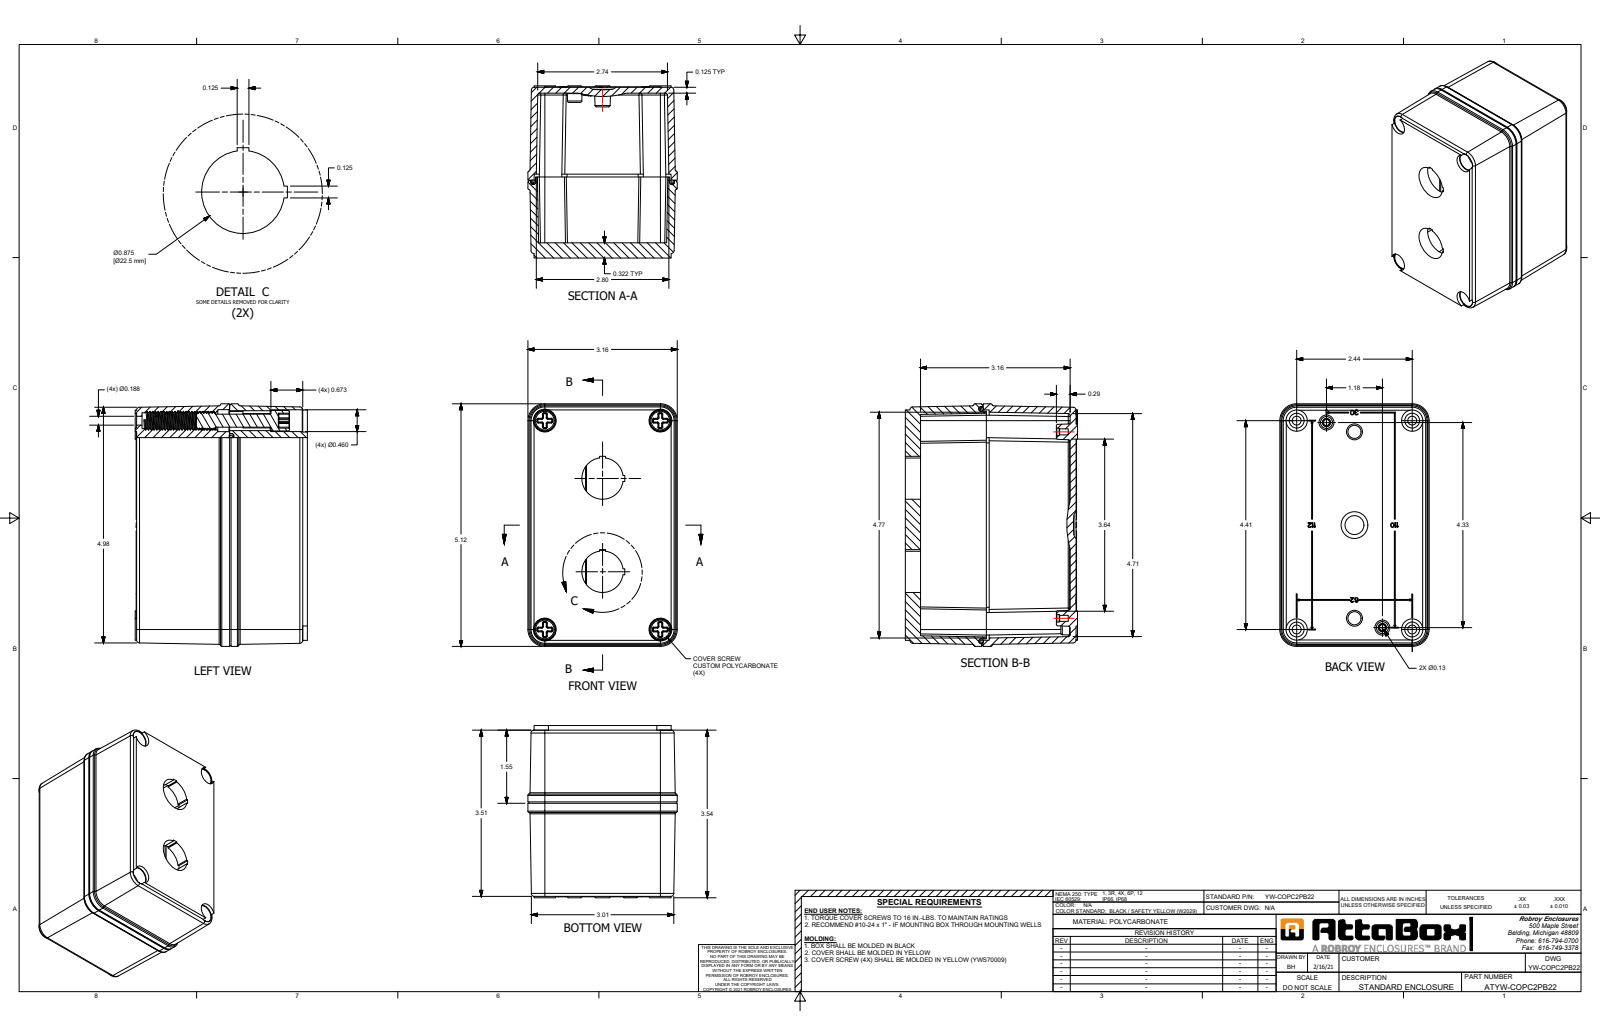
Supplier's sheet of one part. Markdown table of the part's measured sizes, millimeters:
| quantity | value |
| --- | --- |
| part name | YW-COPC2PB22_rev5 |
| STEP written by | SolidWorks 2023 (AUTOMOTIVE_DESIGN) |
| units | millimeters |
| bodies | 7 solids, 1124 faces (282 planar, 410 cylindrical, 432 other) |
| overall size | 130.1 × 92.4 × 80.1 |
| volume | 266 500 mm³ |
| surface area | 128 500 mm² |
| round holes (diameter × count) | 2.5 × 6, 4 × 4, 4.7 × 4, 8 × 4, 8.4 × 4, 11.7 × 4, 11.8 × 4, 3.2 × 2, 3.2 × 2, 22.2 × 1 |
| round bosses / shafts (diameter × count) | 11.4 × 4, 11 × 4, 7 × 4, 8 × 2, 2.5 × 2, 8.1 × 1 |
| partial cylindrical surfaces (radius × count) | 0.5 × 50, 0.3 × 32, 0.4 × 16, 0.8 × 16, 1.6 × 11, 1 × 8, 2 × 8, 2.8 × 8 |
| main face-to-face distances | 3.4, 4.1, 91.6, 4.2, 87.5, 78.1, 74.7, 83.4, 79.3, 8.2 |
| hole center spacings | 31.6, 110.4, 14.5, 15.8, 16, 43.8, 46, 62 |
